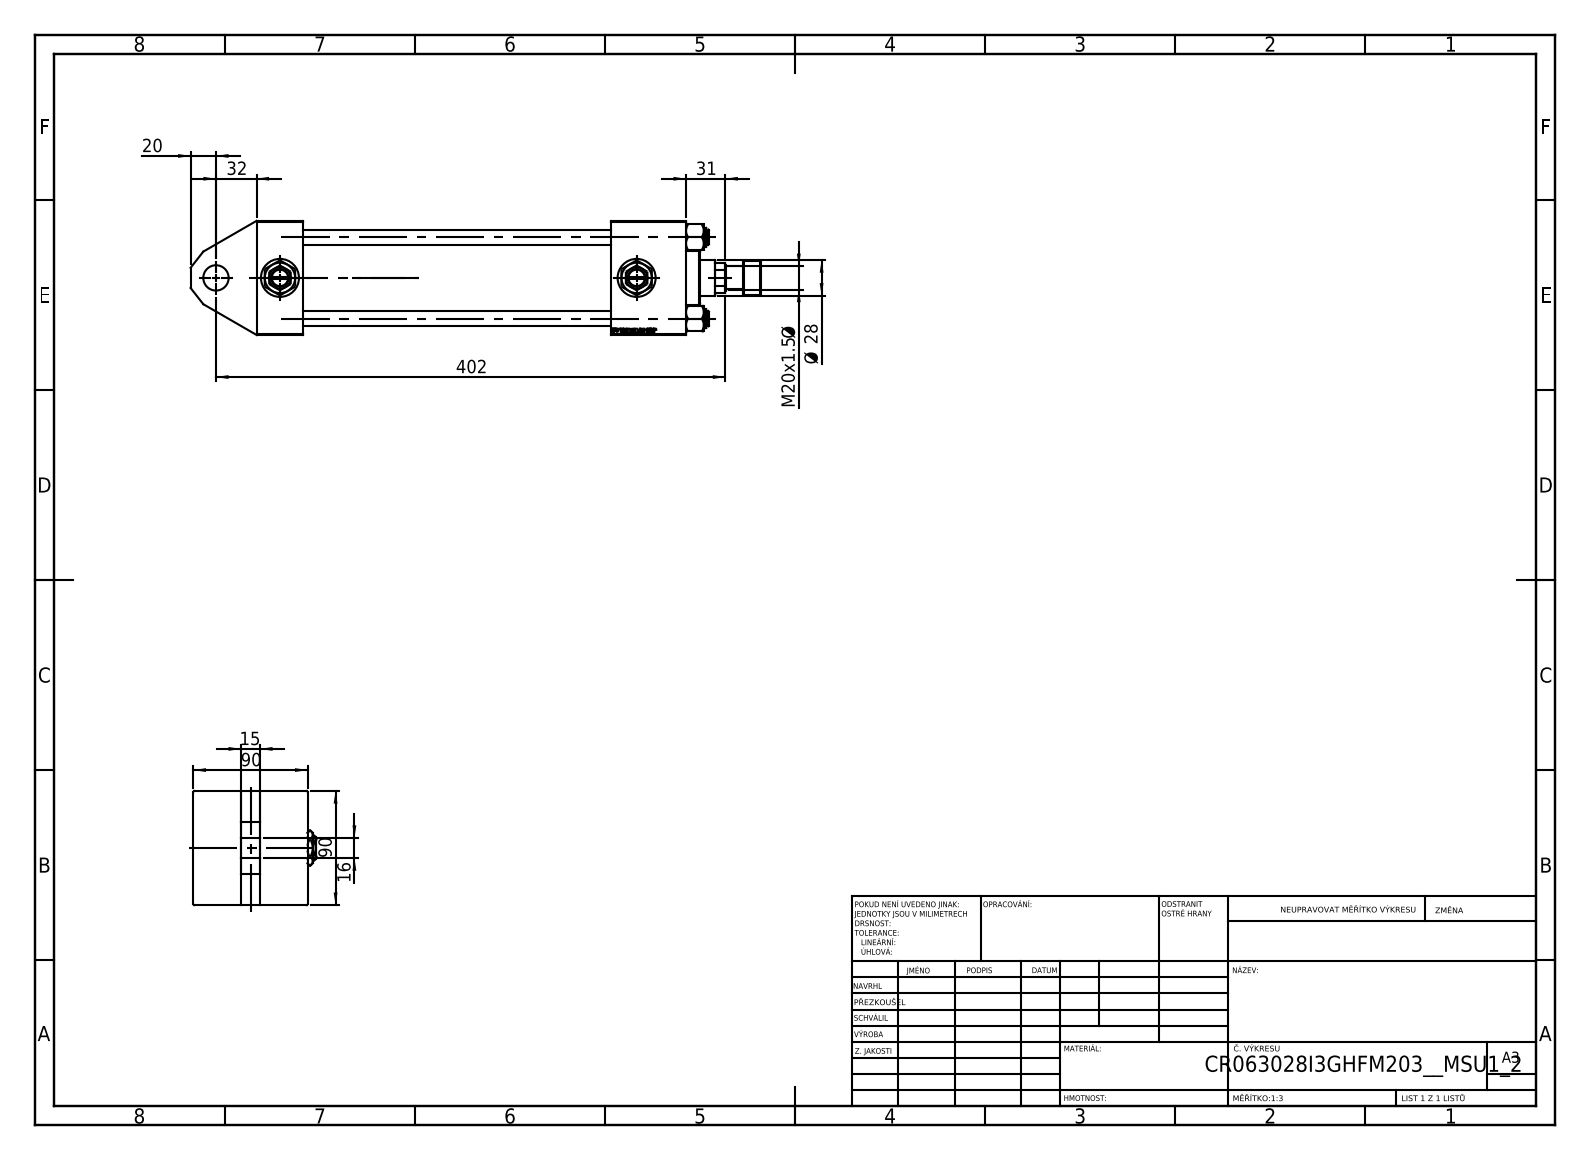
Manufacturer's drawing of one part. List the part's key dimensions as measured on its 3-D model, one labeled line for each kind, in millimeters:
Part name (STEP PRODUCT): NUT_M5_I; V215CR_I_Body; V215CR_ROD_END_F; V215CR_VCP_I (+3 more)
STEP written by: SolidWorks 2019 (CONFIG_CONTROL_DESIGN)
Units: millimetres
Bodies: 14 solids, 1194 faces (554 planar, 96 cylindrical, 544 other)
Overall size (bounding box): 450 × 97 × 90
Volume: 1 315 000 mm³ · Surface area: 317 773 mm²
Round holes (diameter × count): ⌀12 ×4, ⌀7 ×2, ⌀20.96 ×2, ⌀30 ×2, ⌀18.5 ×1, ⌀20 ×1, ⌀28 ×1, ⌀31 ×1, ⌀50 ×1, ⌀60 ×1, ⌀63 ×1
Round bosses / shafts (diameter × count): ⌀15 ×4, ⌀69 ×1, ⌀42 ×1, ⌀27 ×1, ⌀18 ×1
Main face-to-face distances: 90, 37, 339, 302, 59, 37.5, 52.5, 280, 243, 310.3
Hole centre spacings: 45.47, 64.3, 90.93, 50.5, 281.5, 332
